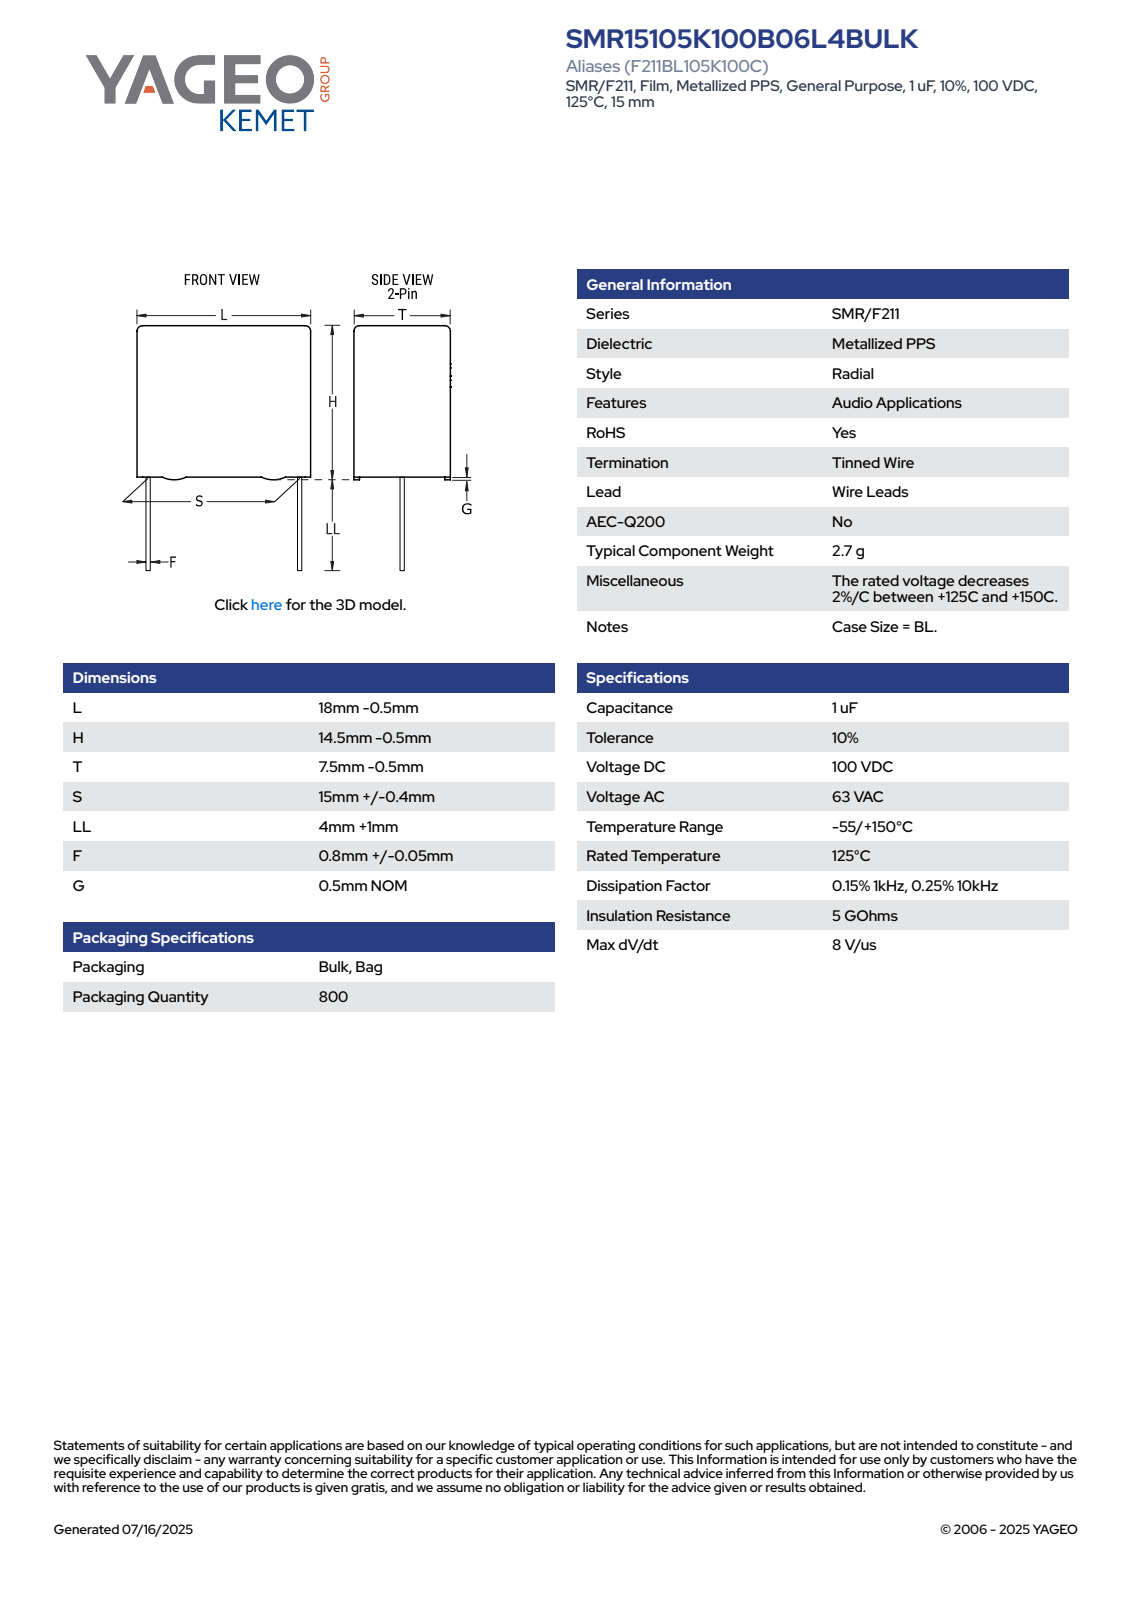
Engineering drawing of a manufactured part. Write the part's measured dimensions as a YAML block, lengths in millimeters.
part_name: "CFR_RBG_18X14.5X7.5_L17.5H14T7S15LL5F0.85G0.5"
step_written_by: "SolidWorks 2021 (AUTOMOTIVE_DESIGN)"
units: millimeters
bodies: {solids: 4, faces: 89, planar: 81, cylindrical: 8, other: 0}
overall_size: [19, 17.5, 7]
volume: 1660
surface_area: 971
round_bosses_or_shafts:
  - {diameter: 0.85, count: 2}
partial_cylinders:
  - {radius: 0.5, count: 4}
face_to_face_distances: [7, 13.5, 17.5, 0.4, 6.6, 0.5, 14, 6.2, 5.5, 5]
